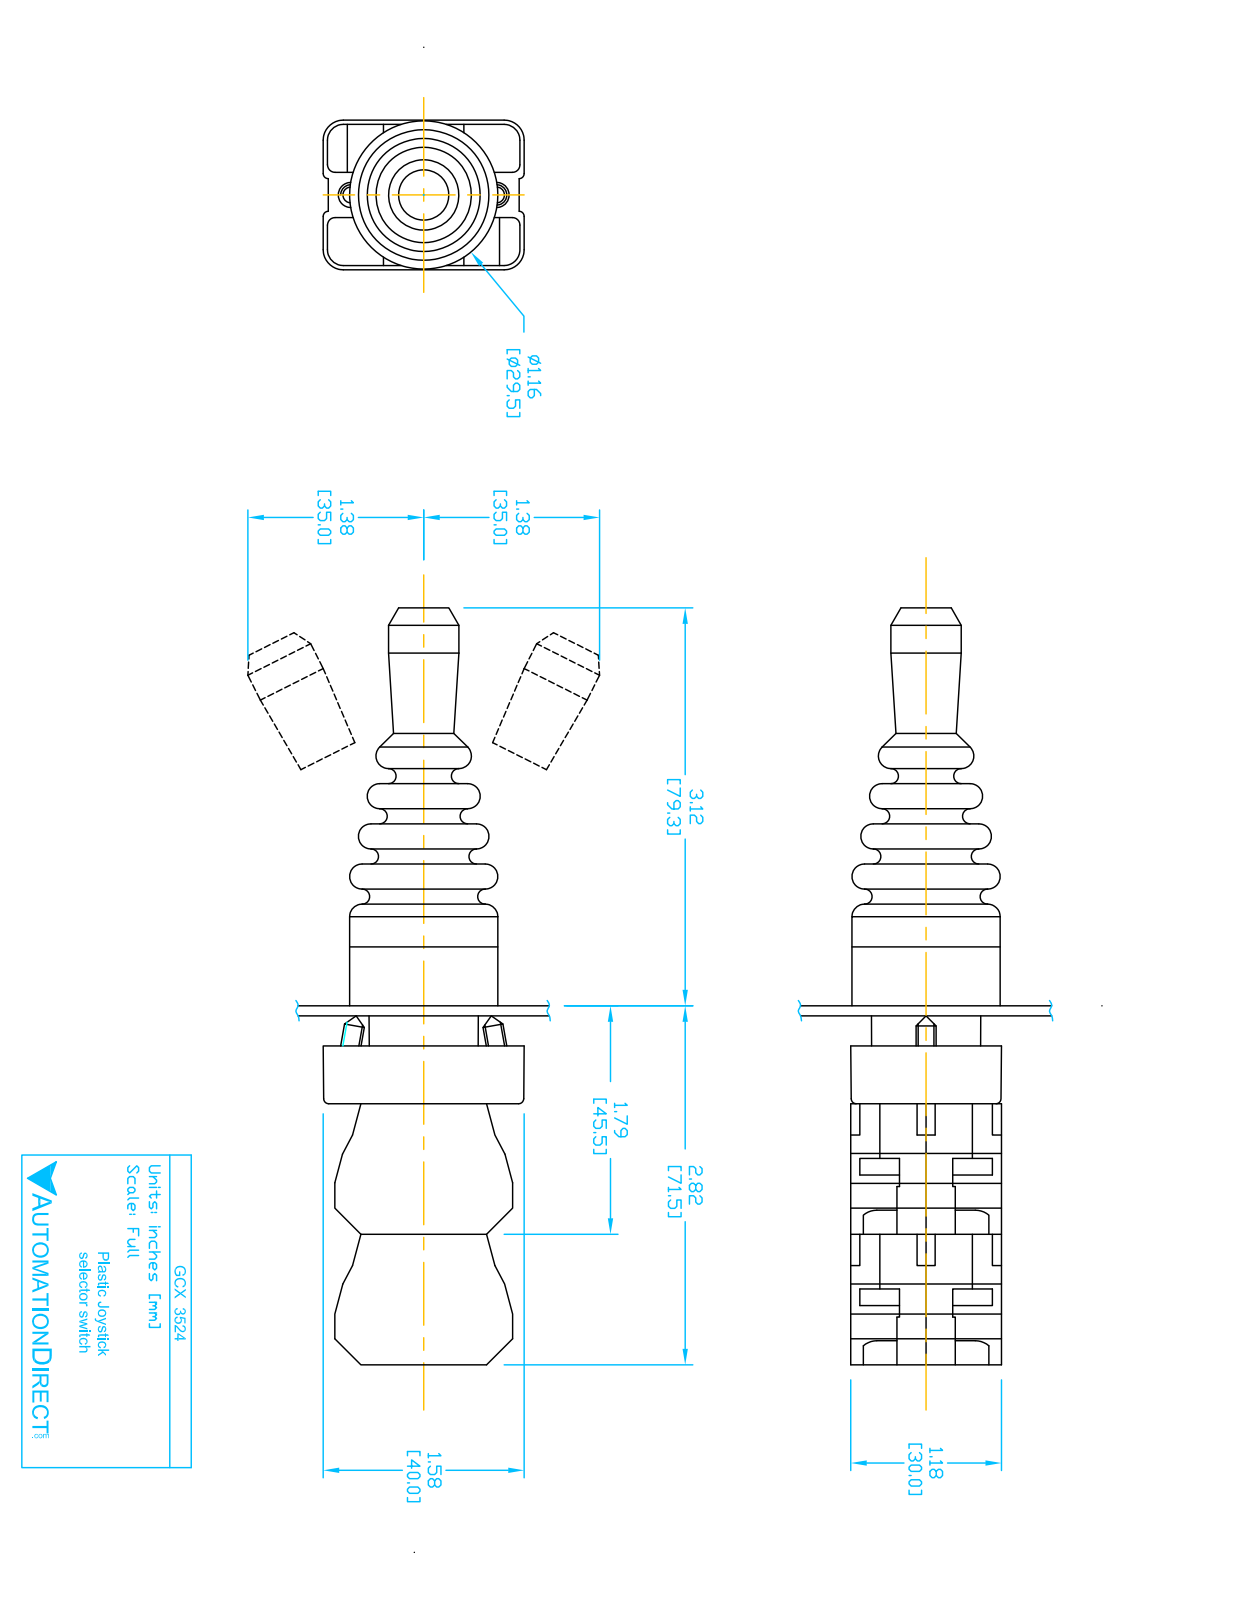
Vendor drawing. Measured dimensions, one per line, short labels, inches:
name: ECX3524
written by: SolidWorks 2017 (AUTOMOTIVE_DESIGN)
unit: in
bodies: 9 solids, 707 faces (450 planar, 172 cylindrical, 85 other)
size: 5.909 × 1.581 × 1.181
volume: 4.87 in³; area: 51.32 in²
holes: 4× ⌀0.079, 2× ⌀0.087, 2× ⌀0.124, 2× ⌀0.13, 1× ⌀0.197, 1× ⌀0.878, 1× ⌀0.888
bosses: 2× ⌀0.157, 1× ⌀1.181, 1× ⌀1.175, 1× ⌀0.945, 1× ⌀0.856, 1× ⌀0.78
rounds: 24× R0.059, 12× R0.041, 12× R0.124, 12× R0.157, 4× R0.02, 4× R0.039, 2× R0.063, 2× R0.079
face distances: 0.579, 0.598, 1.024, 0.02, 1.177, 1.193, 2.217, 0.018, 0.037, 0.031
hole spacings: 0.236, 0.98, 0.472, 0.544, 1.004, 1.013, 0.49, 0.491
